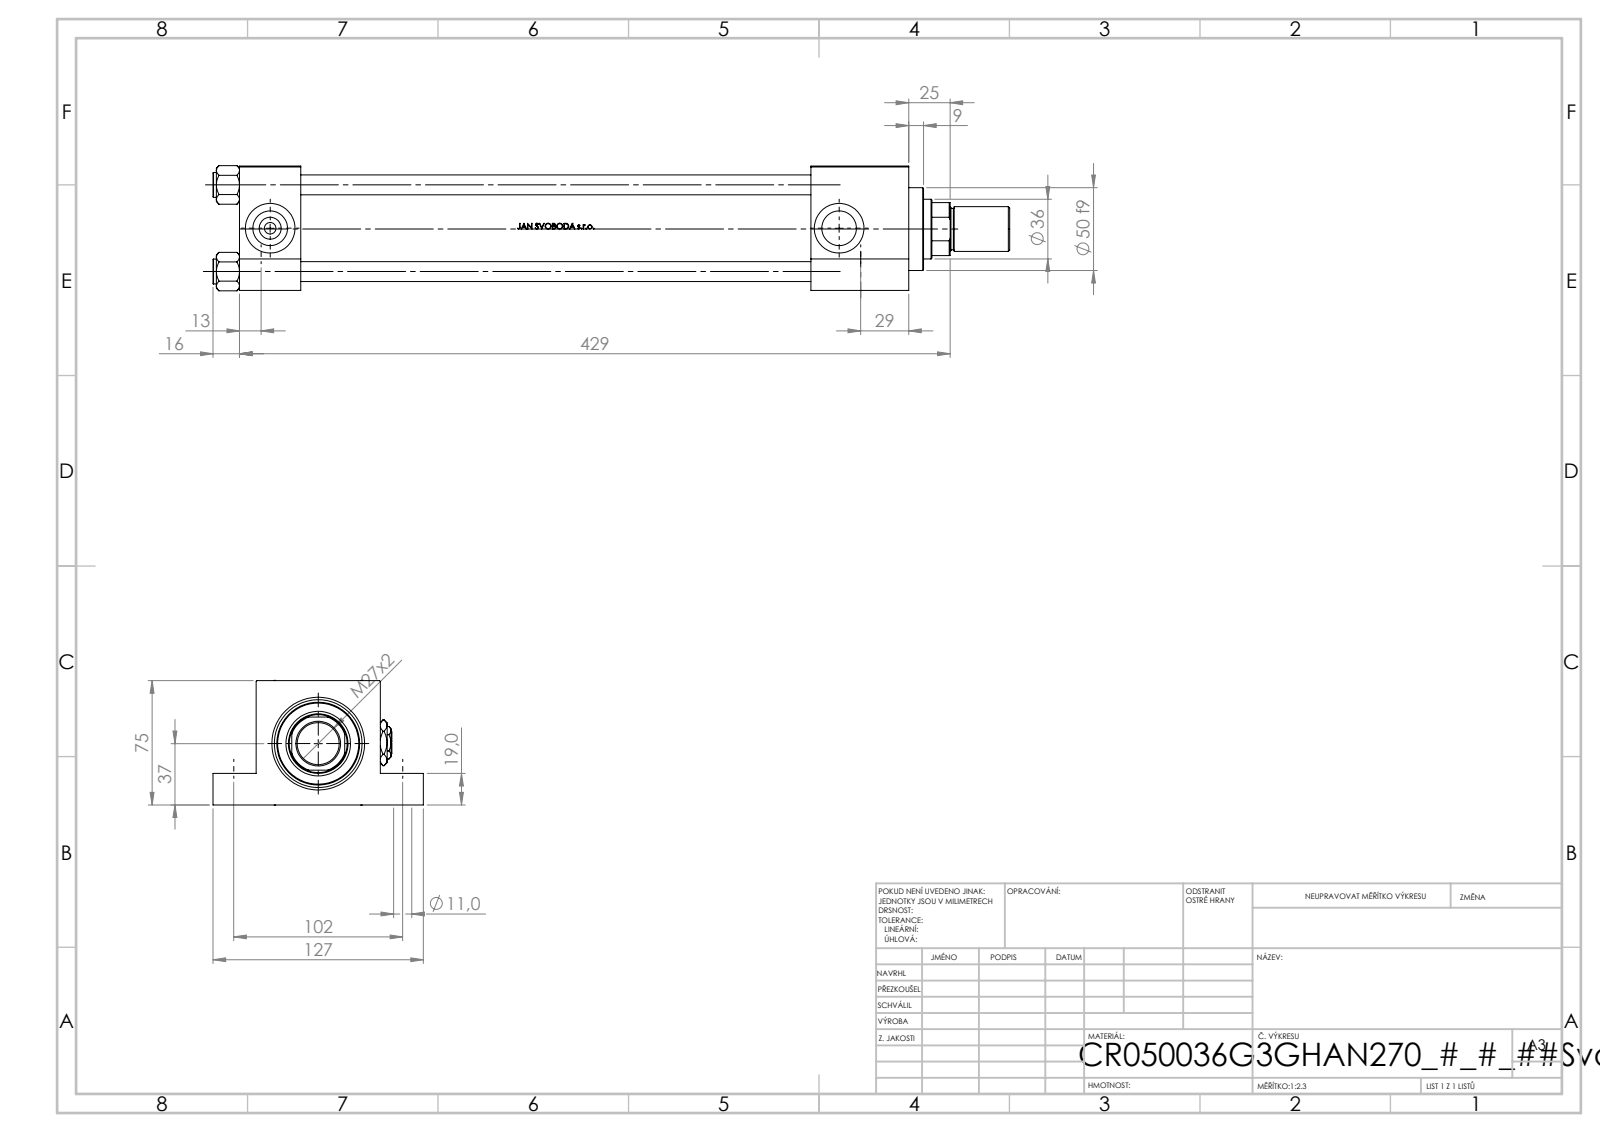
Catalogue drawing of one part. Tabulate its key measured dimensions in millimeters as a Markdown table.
| quantity | value |
| --- | --- |
| part name | NUT_M5_G; V215CR_VCP_G; V215CR_G_TYCINKA; Zatka_pro_OIL_PORT (+3 more) |
| STEP written by | SolidWorks 2019 (CONFIG_CONTROL_DESIGN) |
| units | millimeters |
| bodies | 14 solids, 1197 faces (481 planar, 136 cylindrical, 580 other) |
| overall size | 481 × 127 × 75.54 |
| volume | 1 292 000 mm³ |
| surface area | 325 613 mm² |
| round holes (diameter × count) | 11 × 4, 12 × 4, 7 × 2, 20.96 × 2, 30 × 2, 25.5 × 1, 36 × 1, 39 × 1, 41 × 1, 53 × 1 |
| round bosses / shafts (diameter × count) | 15 × 4, 56 × 1, 50 × 1, 27 × 1, 25 × 1 |
| partial cylindrical surfaces (radius × count) | 17.5 × 1 |
| main face-to-face distances | 75, 37, 19, 56, 404, 367, 59, 345, 308, 26 |
| hole center spacings | 52.3, 36.63, 37.34, 73.96, 102, 362, 376.1, 343.5 |
